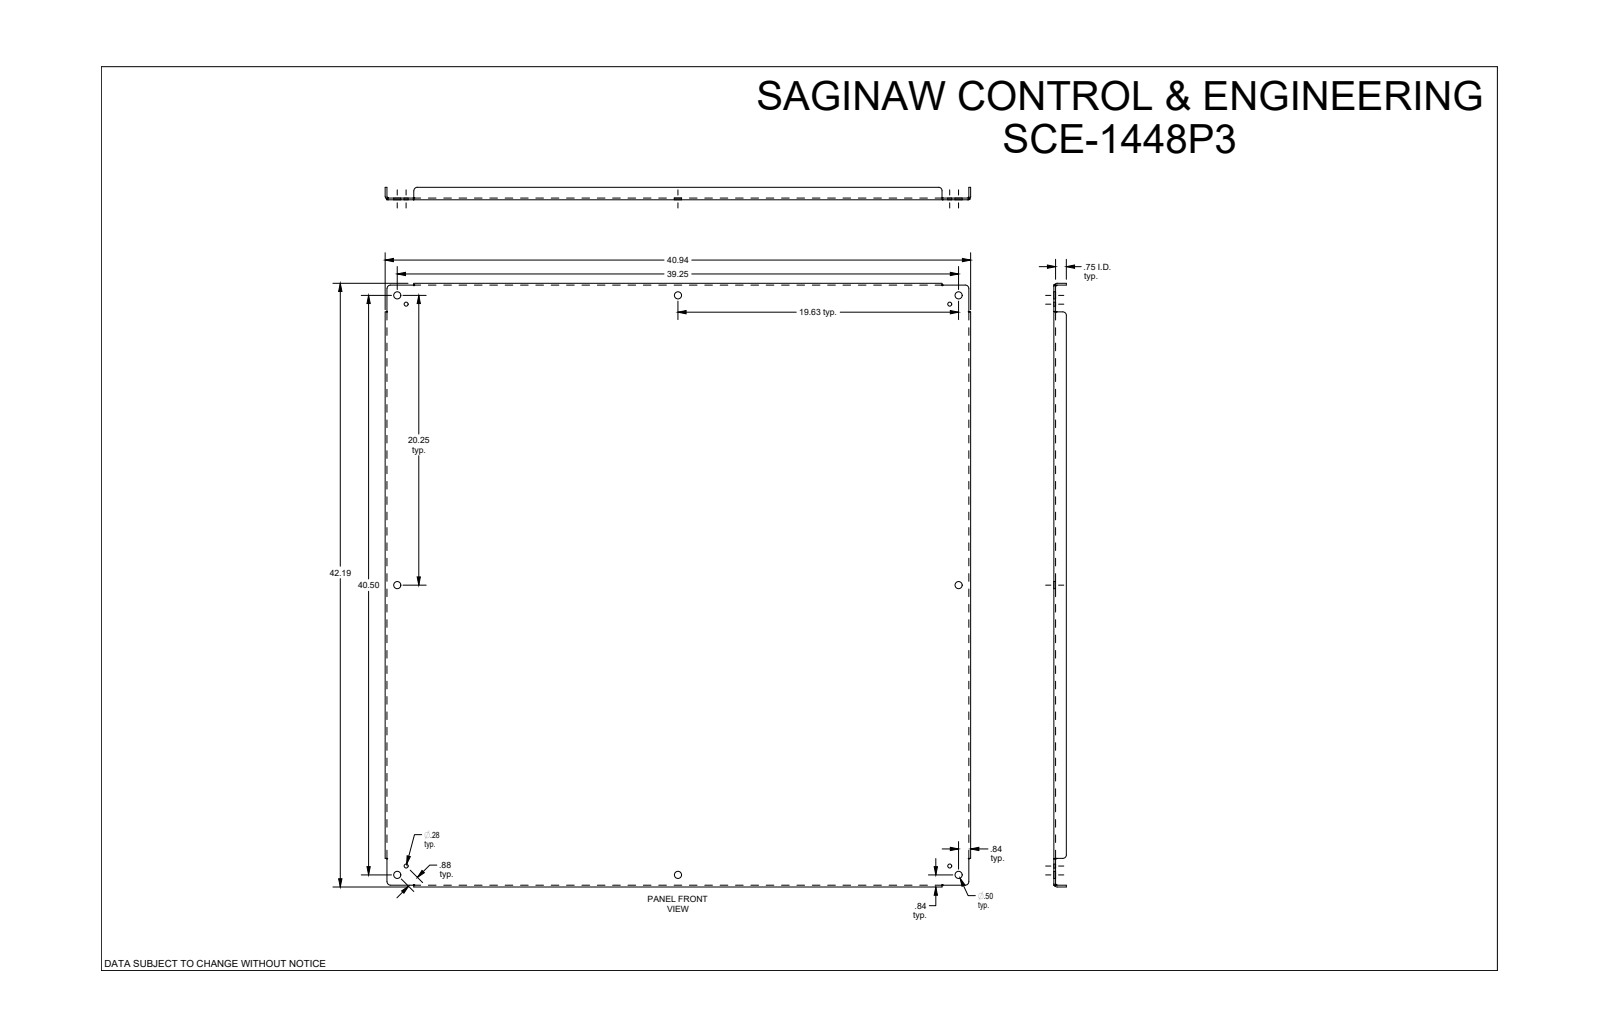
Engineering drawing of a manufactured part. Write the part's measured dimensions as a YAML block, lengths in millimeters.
part_name: "SCE-1448P3"
step_written_by: "SolidWorks 2019 (CONFIG_CONTROL_DESIGN)"
units: millimeters
bodies: {solids: 1, faces: 86, planar: 30, cylindrical: 32, other: 24}
overall_size: [1071.6, 1039.8, 22.2]
volume: 3738000
surface_area: 2369000
round_holes:
  - {diameter: 12.7, count: 8}
  - {diameter: 7.1, count: 4}
partial_cylinders:
  - {radius: 6.4, count: 8}
  - {radius: 2.8, count: 4}
  - {radius: 6, count: 4}
face_to_face_distances: [3.2, 3.2, 1036.7, 1068.4, 1033.4, 1039.8, 1065.2, 1071.5, 19.1, 22.2]
hole_center_spacings: [22.2, 483, 498.5, 498.9, 514.4, 716.3, 981.4, 1013.1]
